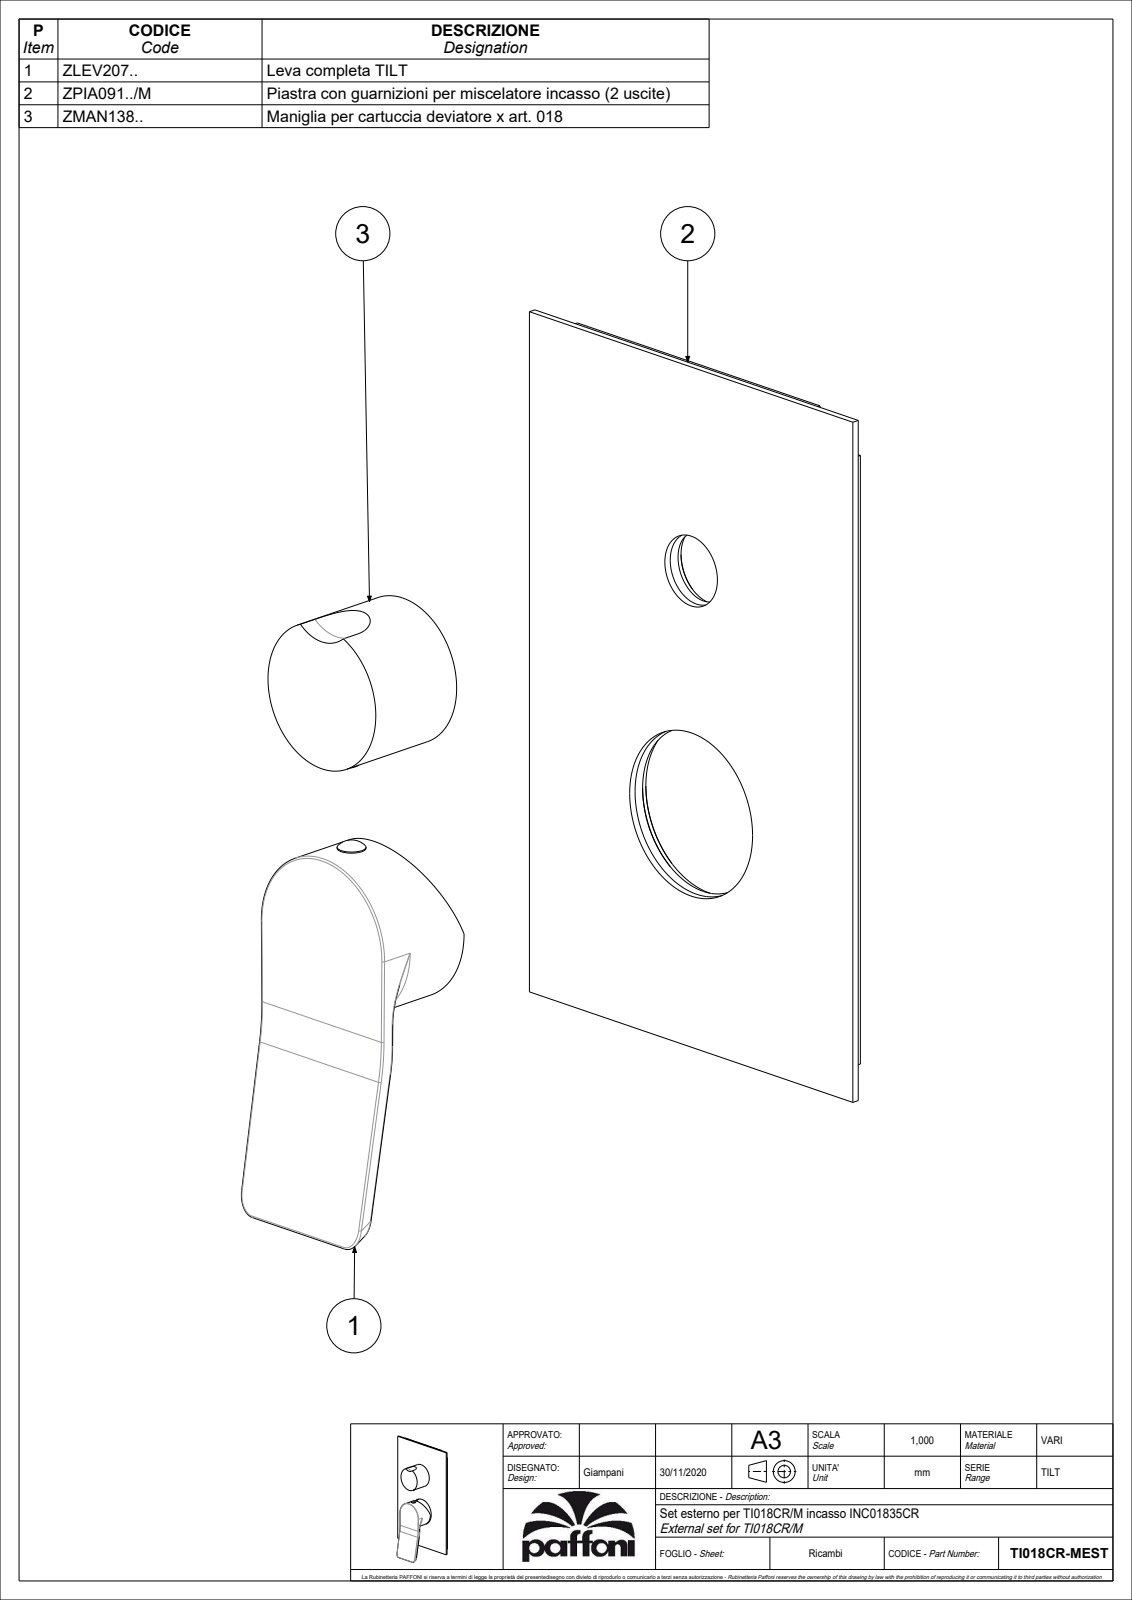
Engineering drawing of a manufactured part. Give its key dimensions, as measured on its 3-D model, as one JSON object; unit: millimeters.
{"part_name": "TI018CR-MEST", "step_written_by": "CREO PARAMETRIC BY PTC INC, 2020044 (CONFIG_CONTROL_DESIGN)", "units": "millimeters", "bodies": {"solids": 3, "faces": 241, "planar": 102, "cylindrical": 81, "other": 58}, "overall_size": [204.58, 120, 48.45], "volume_mm3": 99995, "surface_area_mm2": 75934, "round_holes": [[3, 2], [3.2, 1], [4.2, 1], [14.8, 1], [19.5, 1], [21.5, 1], [25, 1], [36, 1], [45.6, 1], [47.6, 1], [51.1, 1]], "round_bosses_or_shafts": [[7.6, 2], [5.5, 2], [54.6, 1], [45.5, 1], [40, 1], [28.5, 1], [24, 1], [5, 1]], "partial_cylinders_radius": [[0.5, 10], [1.5, 2], [5, 2], [12.5, 1], [44.14, 1], [63, 1]], "face_to_face_distances": [2, 0.8, 2.8, 4.01, 34, 34.8, 32, 4, 30, 16], "hole_center_spacings": [1, 10, 68, 78]}
